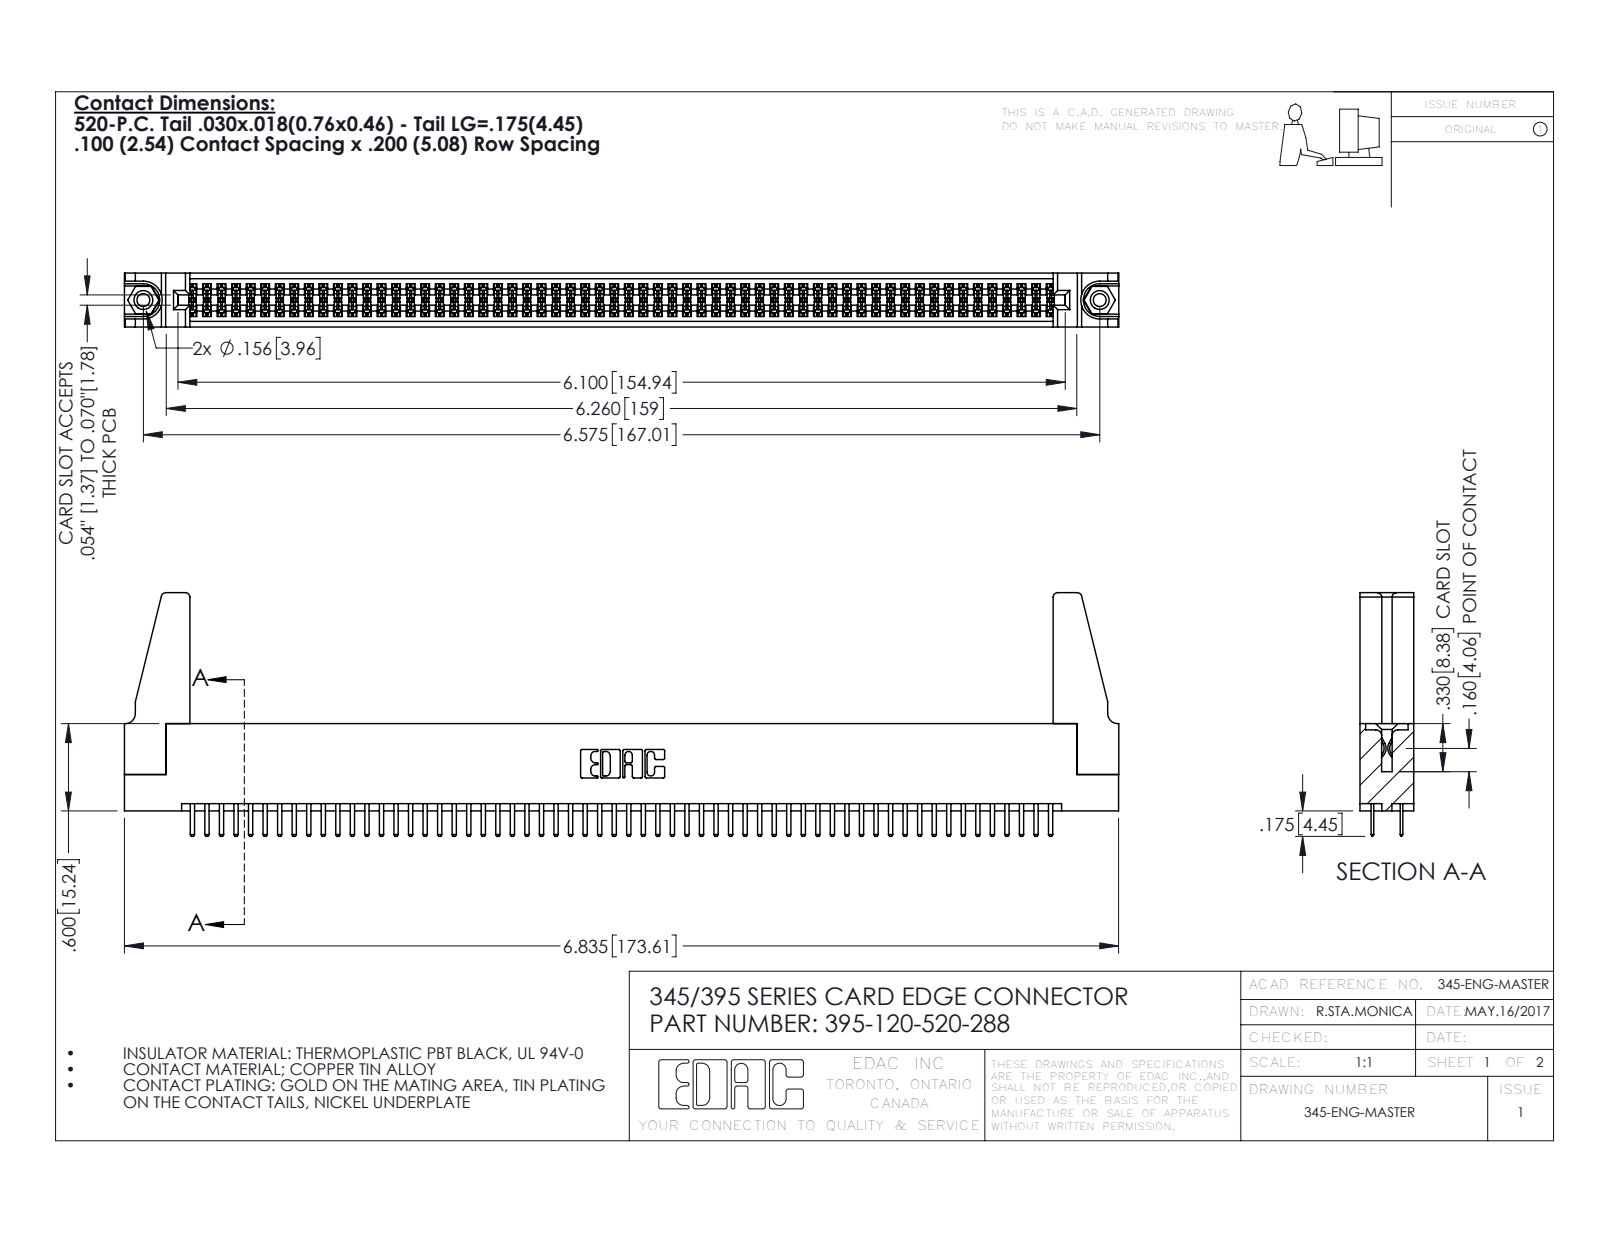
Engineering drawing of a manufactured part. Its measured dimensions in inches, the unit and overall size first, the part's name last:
Units: inches
Overall size (bounding box): 6.836 × 1.675 × 0.37
Round holes (diameter × count): ⌀0.089 ×2, ⌀0.125 ×2, ⌀0.156 ×2, ⌀0.064 ×1
Round bosses / shafts (diameter × count): ⌀0.155 ×2
Partial cylindrical surfaces — rounded edges, fillets, slot ends (radius × count): R0.006 ×180, R0.01 ×124, R0.01 ×22, R0.03 ×8, R0.007 ×6, R0.031 ×6, R0.026 ×3, R0.014 ×2
Main face-to-face distances: 0.072, 0.298, 0.37, 0.2, 0.098, 0.272, 0.025, 0.225, 0.022, 0.072
Hole centre spacings: 0.27, 6.339, 6.575
Volume: 1.235 in³ · Surface area: 44.11 in²
Bodies: 125 solids, 6730 faces (4352 planar, 2362 cylindrical, 16 other)
Part name (STEP PRODUCT): 345 Part_Flush Mounting Lugs - 0.156 Dia-TH; 345-250-001_345-250-001-102; 395-120-520-288; 345-292-001_345-293-120 (+1 more)
STEP written by: SolidWorks 2016 (CONFIG_CONTROL_DESIGN)
